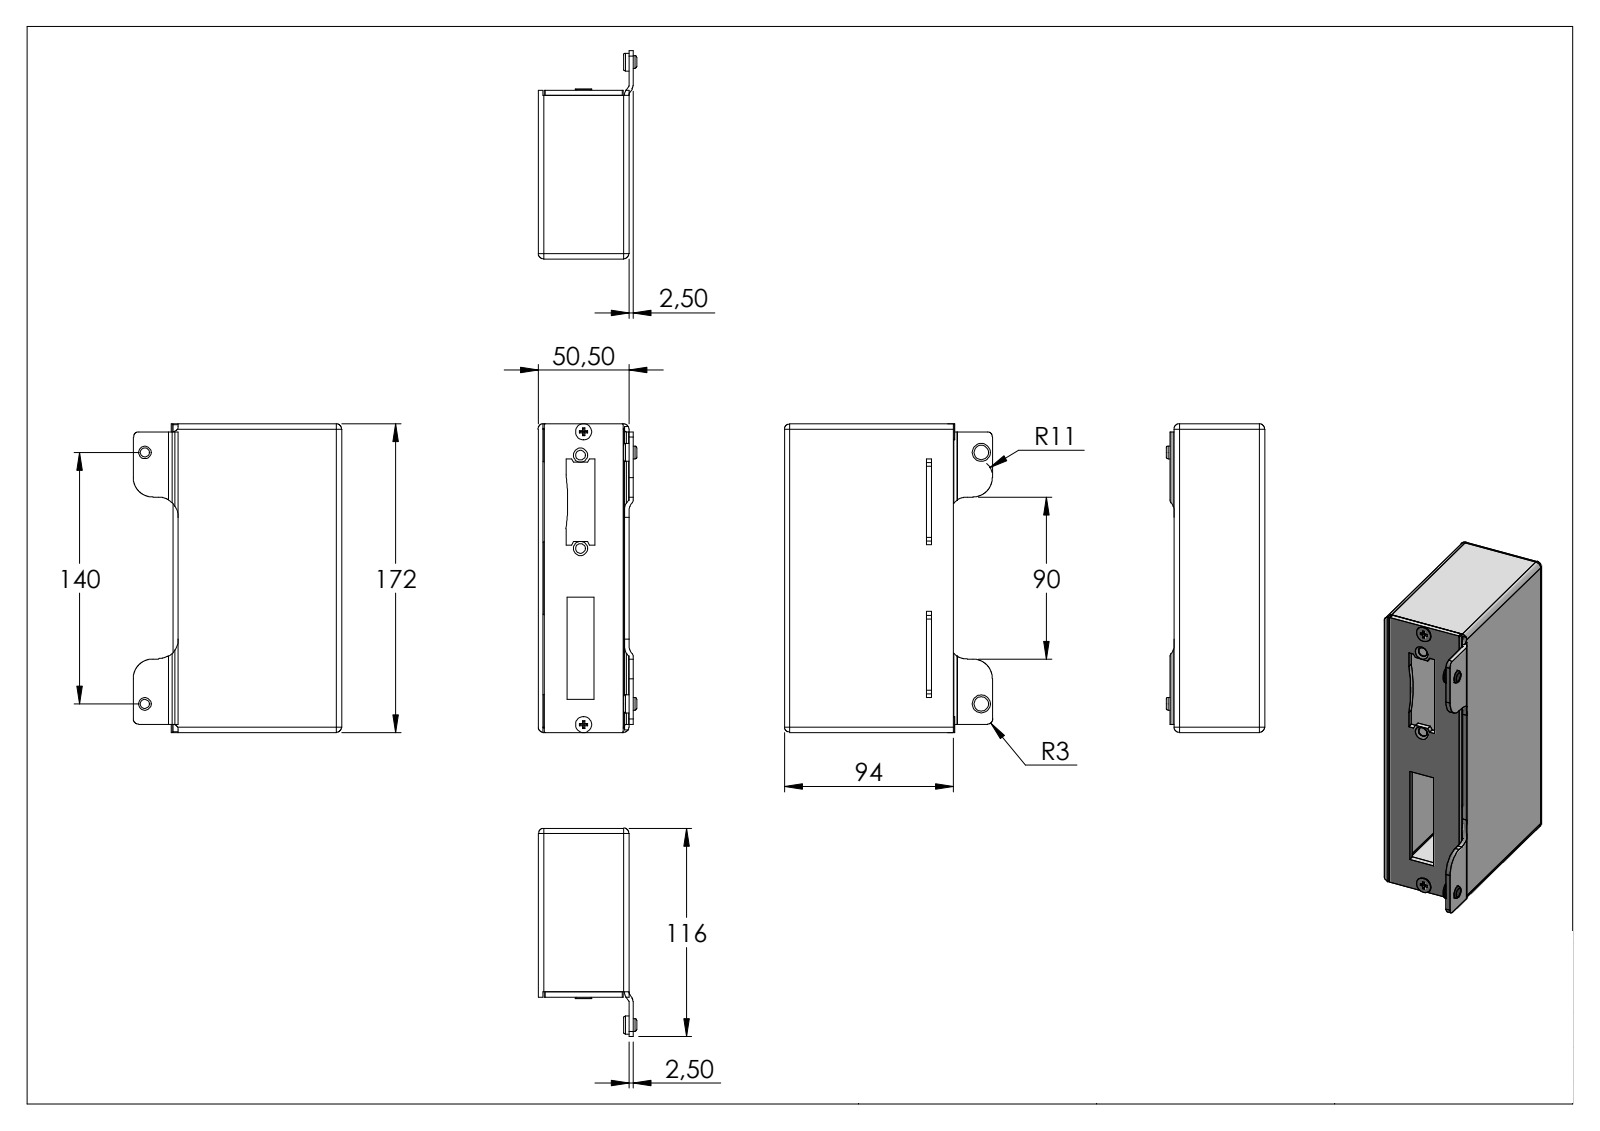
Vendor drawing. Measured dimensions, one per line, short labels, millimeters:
name: 59300-240-XX Teil3_59305-240-50-SB; 59300-240-XX Teil1_59302-240-50 Teil1; 59302-240-50; 59300-240-XX Teil2_5930X-XXX-XX Teil2 (+1 more)
written by: SolidWorks 2018 (CONFIG_CONTROL_DESIGN)
unit: mm
bodies: 6 solids, 724 faces (377 planar, 69 cylindrical, 278 other)
size: 172 × 116 × 55
volume: 143 505 mm³; area: 116 238 mm²
holes: 2× ⌀4.2, 2× ⌀4.8, 2× ⌀5.4, 2× ⌀5.5
bosses: 4× ⌀5, 2× ⌀10, 2× ⌀9, 2× ⌀7, 2× ⌀4.6
rounds: 26× R3, 13× R0.5, 4× R11, 1× R5.5, 1× R113
face distances: 2.5, 48, 50.5, 45.5, 169.5, 3, 91, 88.5, 94, 91.5
hole spacings: 13.11, 52, 65.02, 98.01, 140, 150.01, 163
